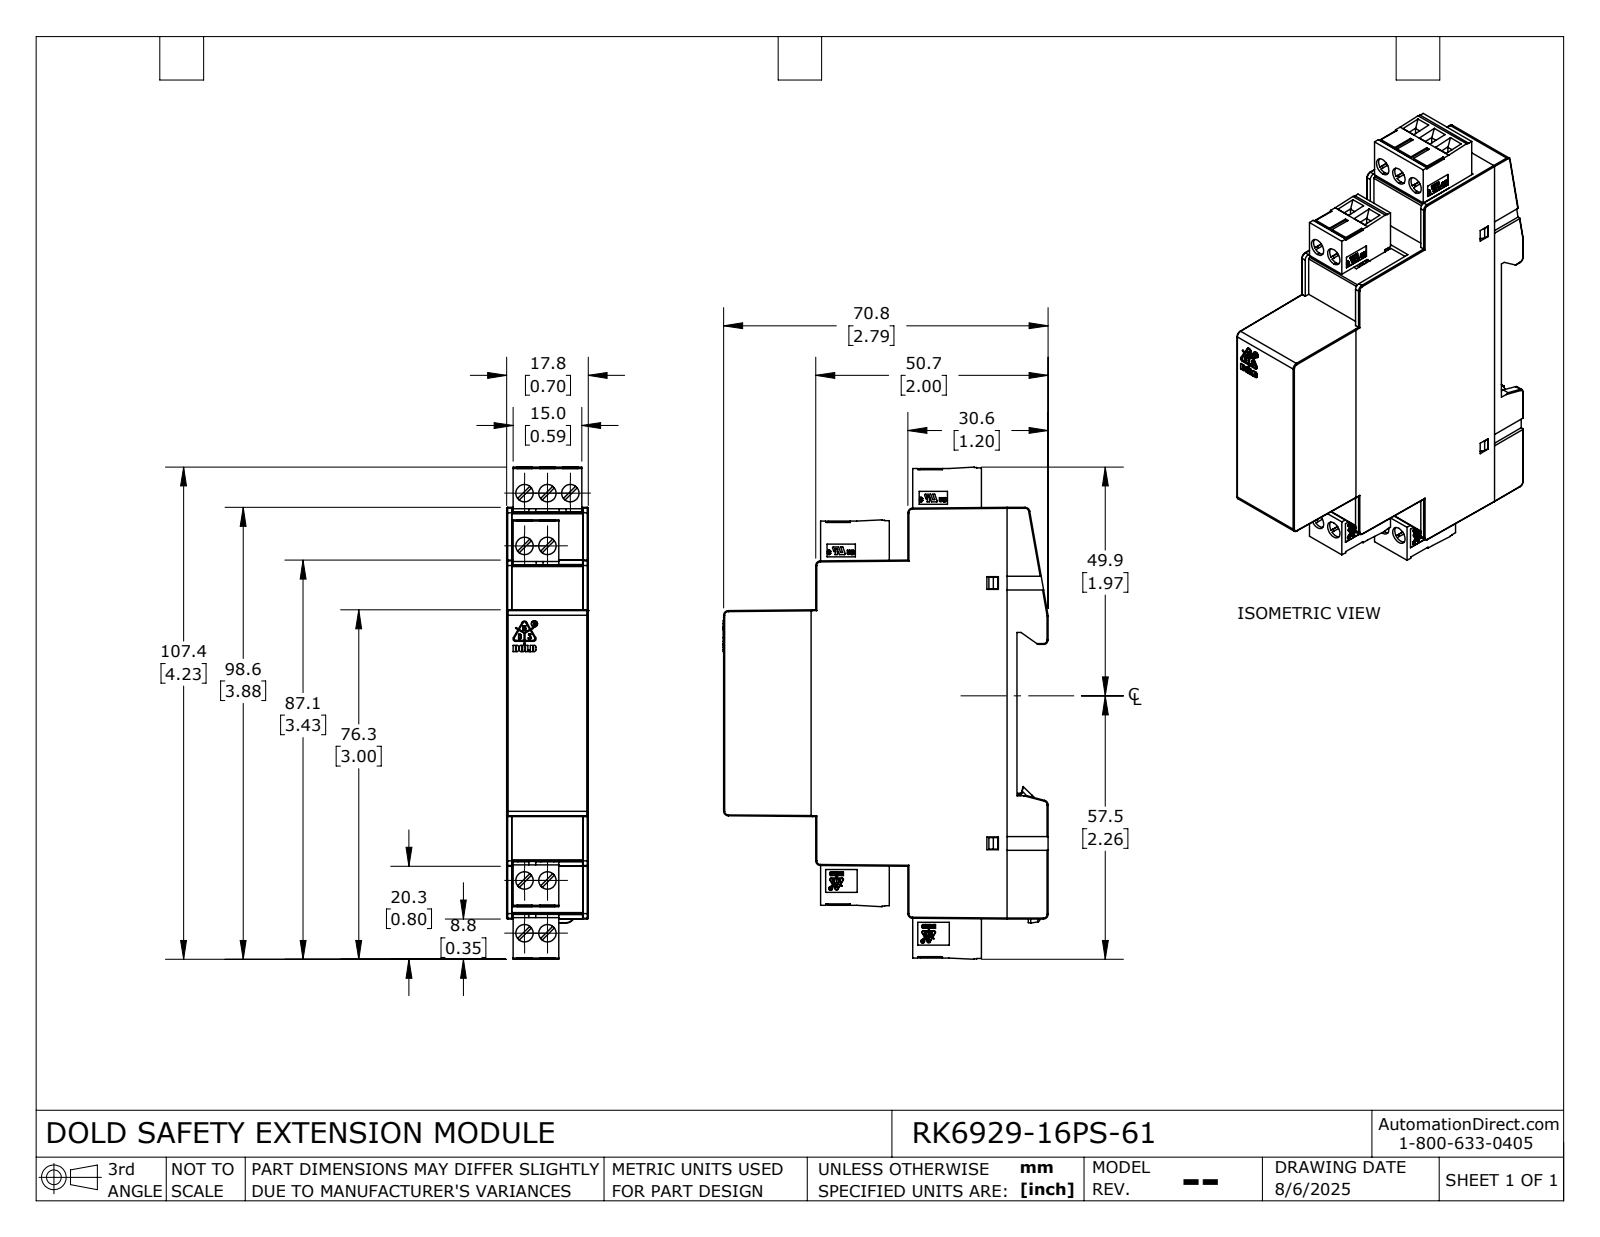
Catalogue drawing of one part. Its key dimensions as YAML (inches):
part_name: "RK6929-16PS-61"
step_written_by: "SolidWorks 2024 (AUTOMOTIVE_DESIGN)"
units: inches
bodies: {solids: 1, faces: 1816, planar: 1353, cylindrical: 391, other: 72}
overall_size: [3.917, 2.791, 0.701]
volume: 5.111
surface_area: 34.09
round_holes:
  - {diameter: 0.15, count: 6}
  - {diameter: 0.138, count: 4}
  - {diameter: 0.03, count: 3}
  - {diameter: 0.05, count: 1}
round_bosses_or_shafts:
  - {diameter: 0.032, count: 3}
  - {diameter: 0.054, count: 1}
partial_cylinders:
  - {radius: 0.008, count: 40}
  - {radius: 0.01, count: 30}
  - {radius: 0.02, count: 23}
  - {radius: 0.039, count: 13}
  - {radius: 0.004, count: 9}
  - {radius: 0.012, count: 9}
  - {radius: 0.016, count: 8}
  - {radius: 0.005, count: 6}
face_to_face_distances: [0.701, 2.52, 0.791, 0.055, 0.646, 0.036, 0.446, 0.449, 0.252, 0.394]
hole_center_spacings: [0.197, 0.453, 0.494, 0.791, 0.815, 2.874, 2.881, 3.327]
